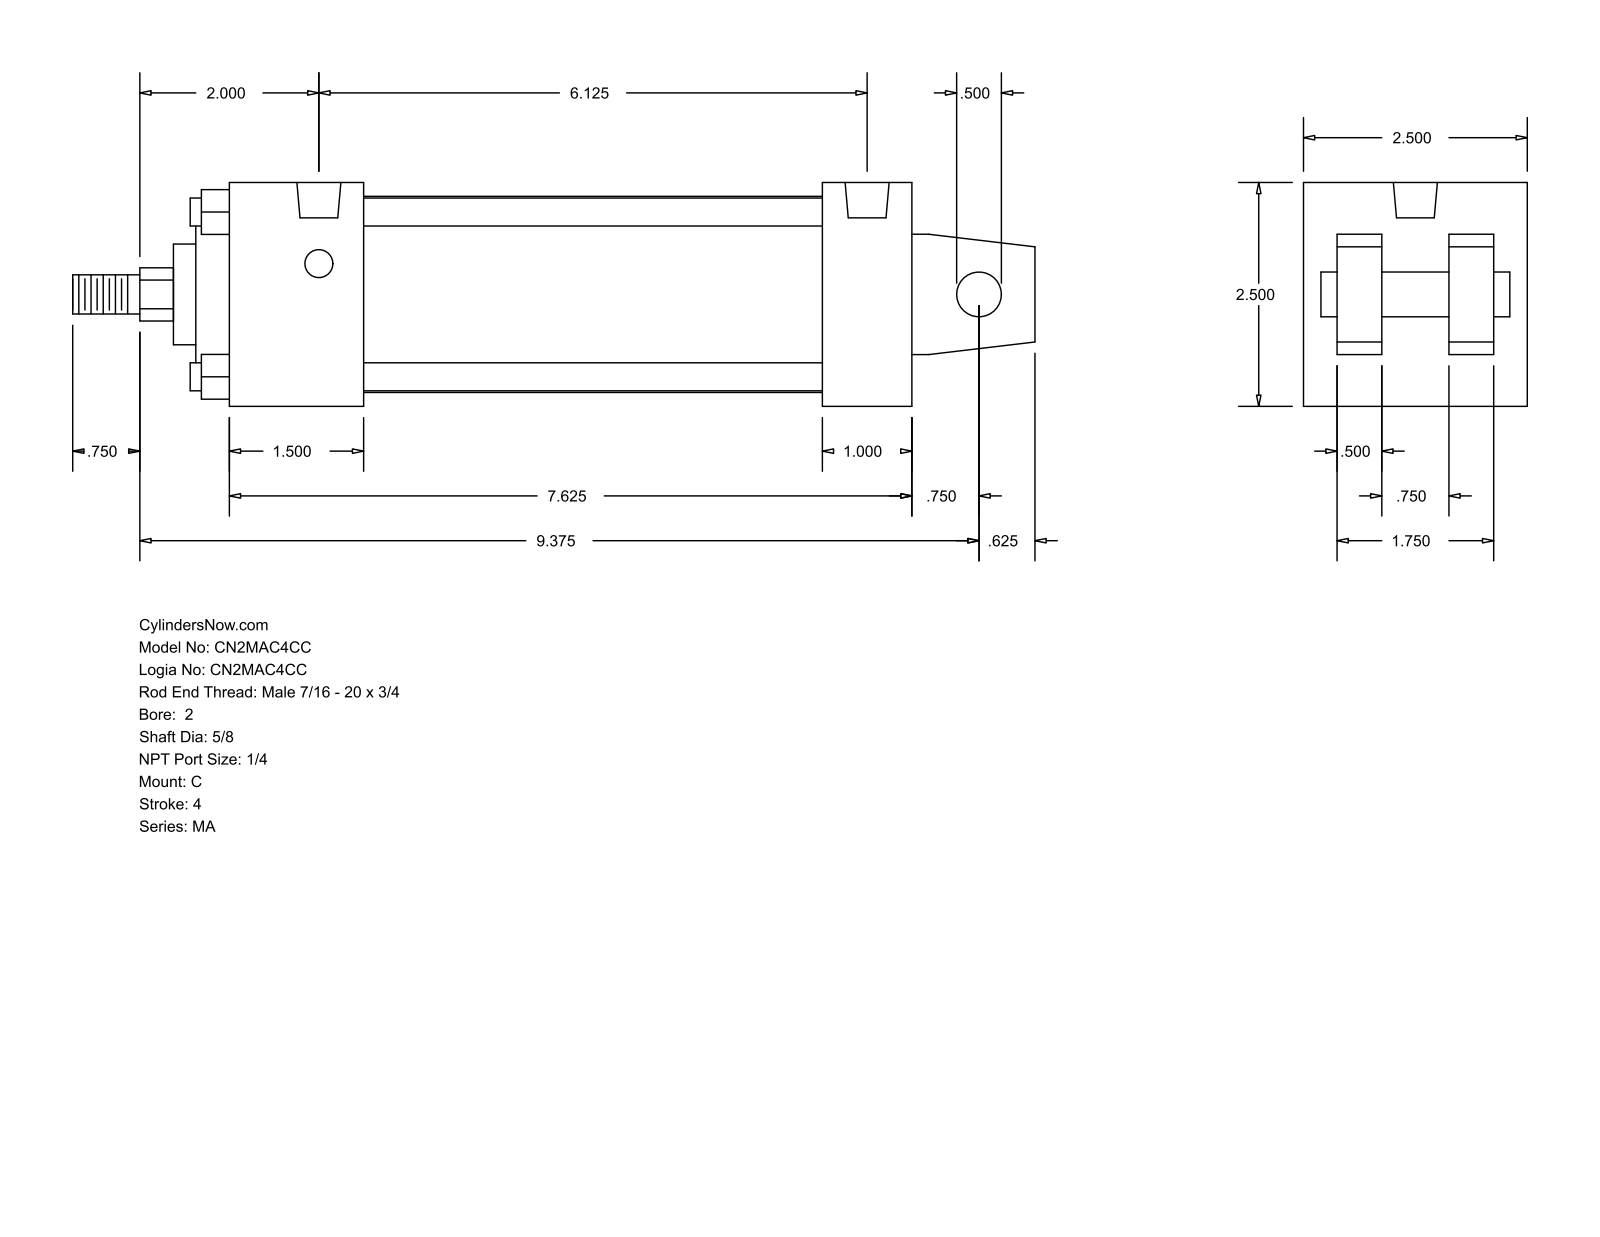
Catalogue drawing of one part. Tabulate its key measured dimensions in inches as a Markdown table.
| quantity | value |
| --- | --- |
| part name | MA_C__0200_0.625 |
| STEP written by | GSSL Pune (CONFIG_CONTROL_DESIGN) |
| units | inches |
| bodies | 0 solids, 105 faces (77 planar, 28 cylindrical, 0 other) |
| overall size | 10.75 × 2.5 × 2.5 |
| round holes (diameter × count) | 0.313 × 4, 0.492 × 2 |
| round bosses / shafts (diameter × count) | 0.313 × 4, 2.19 × 1, 2 × 1, 1.125 × 1, 0.625 × 1, 0.5 × 1, 0.437 × 1 |
| partial cylindrical surfaces (radius × count) | 0.297 × 1 |
| main face-to-face distances | 2.5, 0.375, 0.5, 0.875, 1.625, 2.125, 1.25, 1.5, 7.625, 6.125 |
| hole center spacings | 6.125 |
